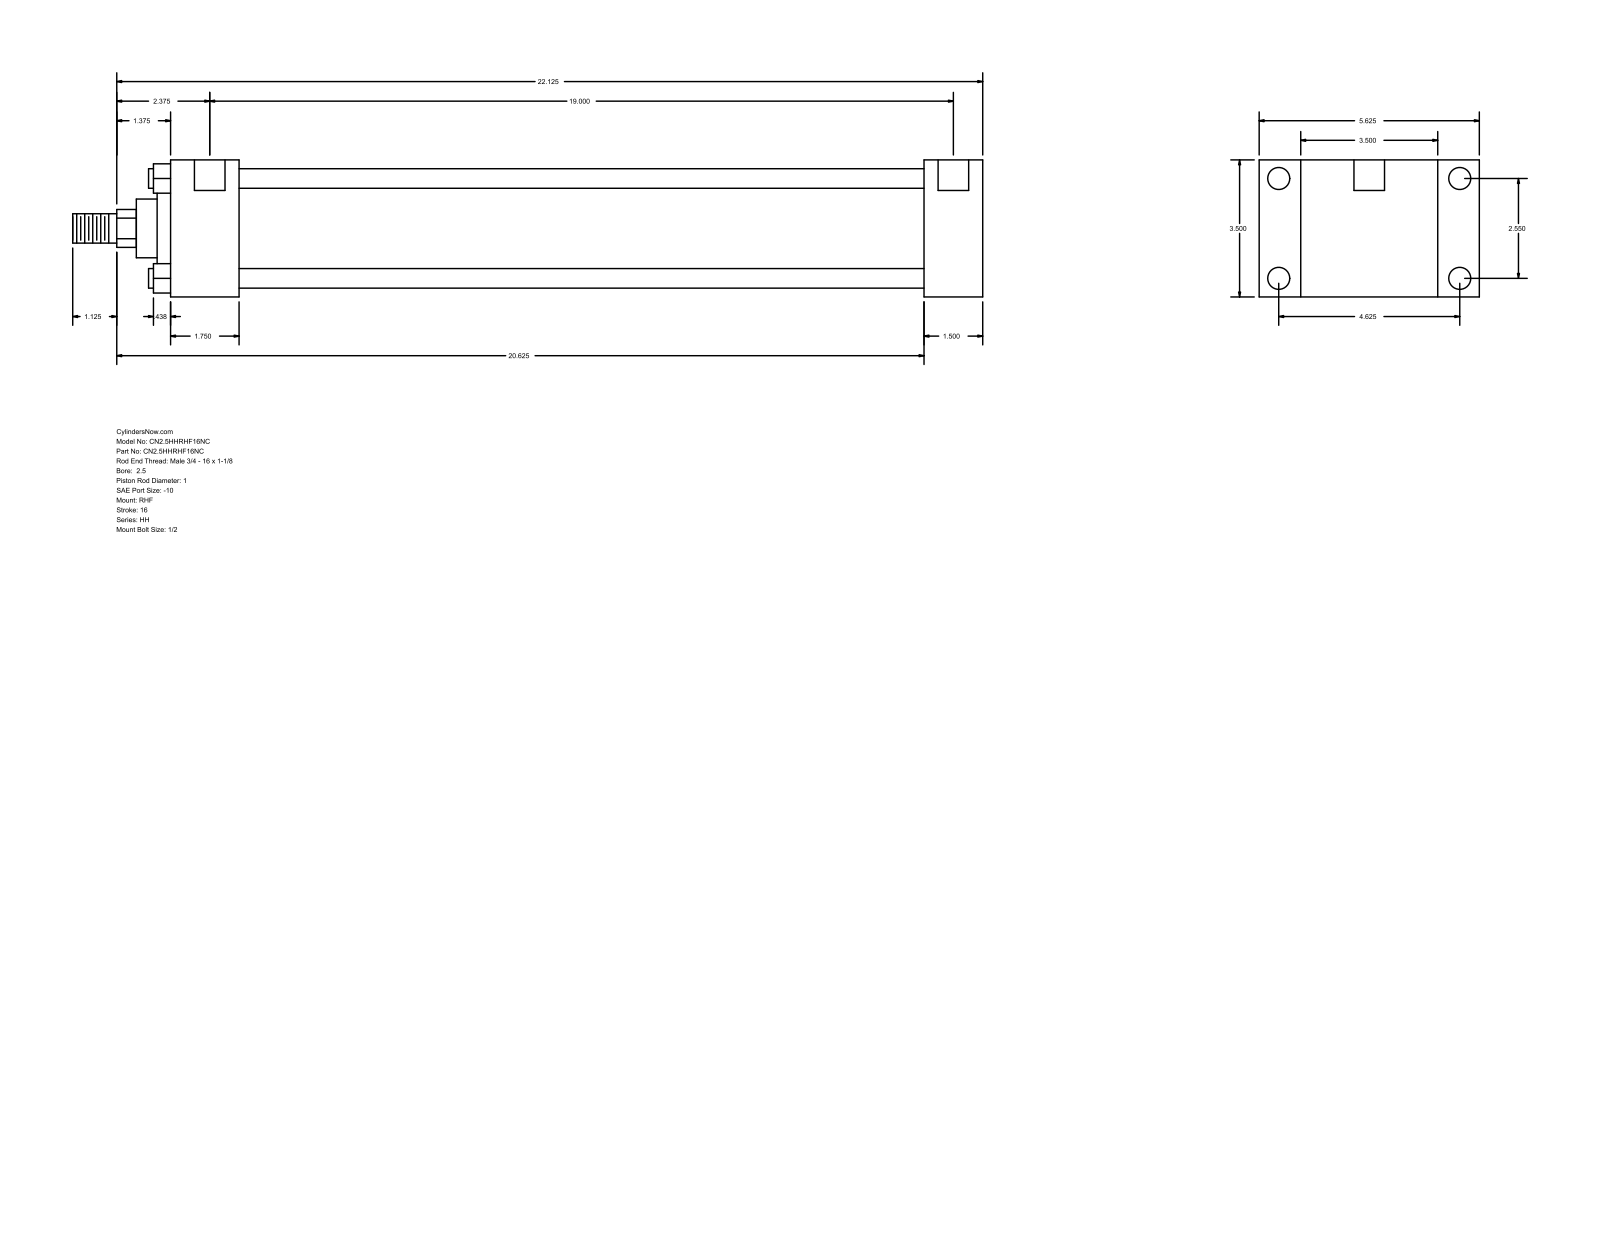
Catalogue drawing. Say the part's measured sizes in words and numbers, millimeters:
The part is named "HH_RHF__0250_1". Its 3-D file was written by "GSSL Pune (CONFIG_CONTROL_DESIGN)". It is 0 solids with 90 faces: 61 planar, 29 cylindrical and 0 other. Overall it measures 590.55 by 142.88 by 88.9 millimeters. Round holes: 4 of diameter 5.56, 4 of diameter 14.3, 2 of diameter 19.84. Round bosses or shafts: 4 of diameter 12.7, 1 of diameter 73.03, 1 of diameter 60.33, 1 of diameter 38.1, 1 of diameter 25.4, 1 of diameter 19.05. Partial cylindrical surfaces (rounded edges, fillets, slot ends): 1 of radius 12.29. The main face-to-face distances are 88.9, 38.1, 26.99, 115.89, 488.96, 527.06, 142.88, 44.46, 444.5, 482.6. The hole center spacings are 1.59, 64.76, 117.48, 134.15, 484.18, 485.77, 482.59.
